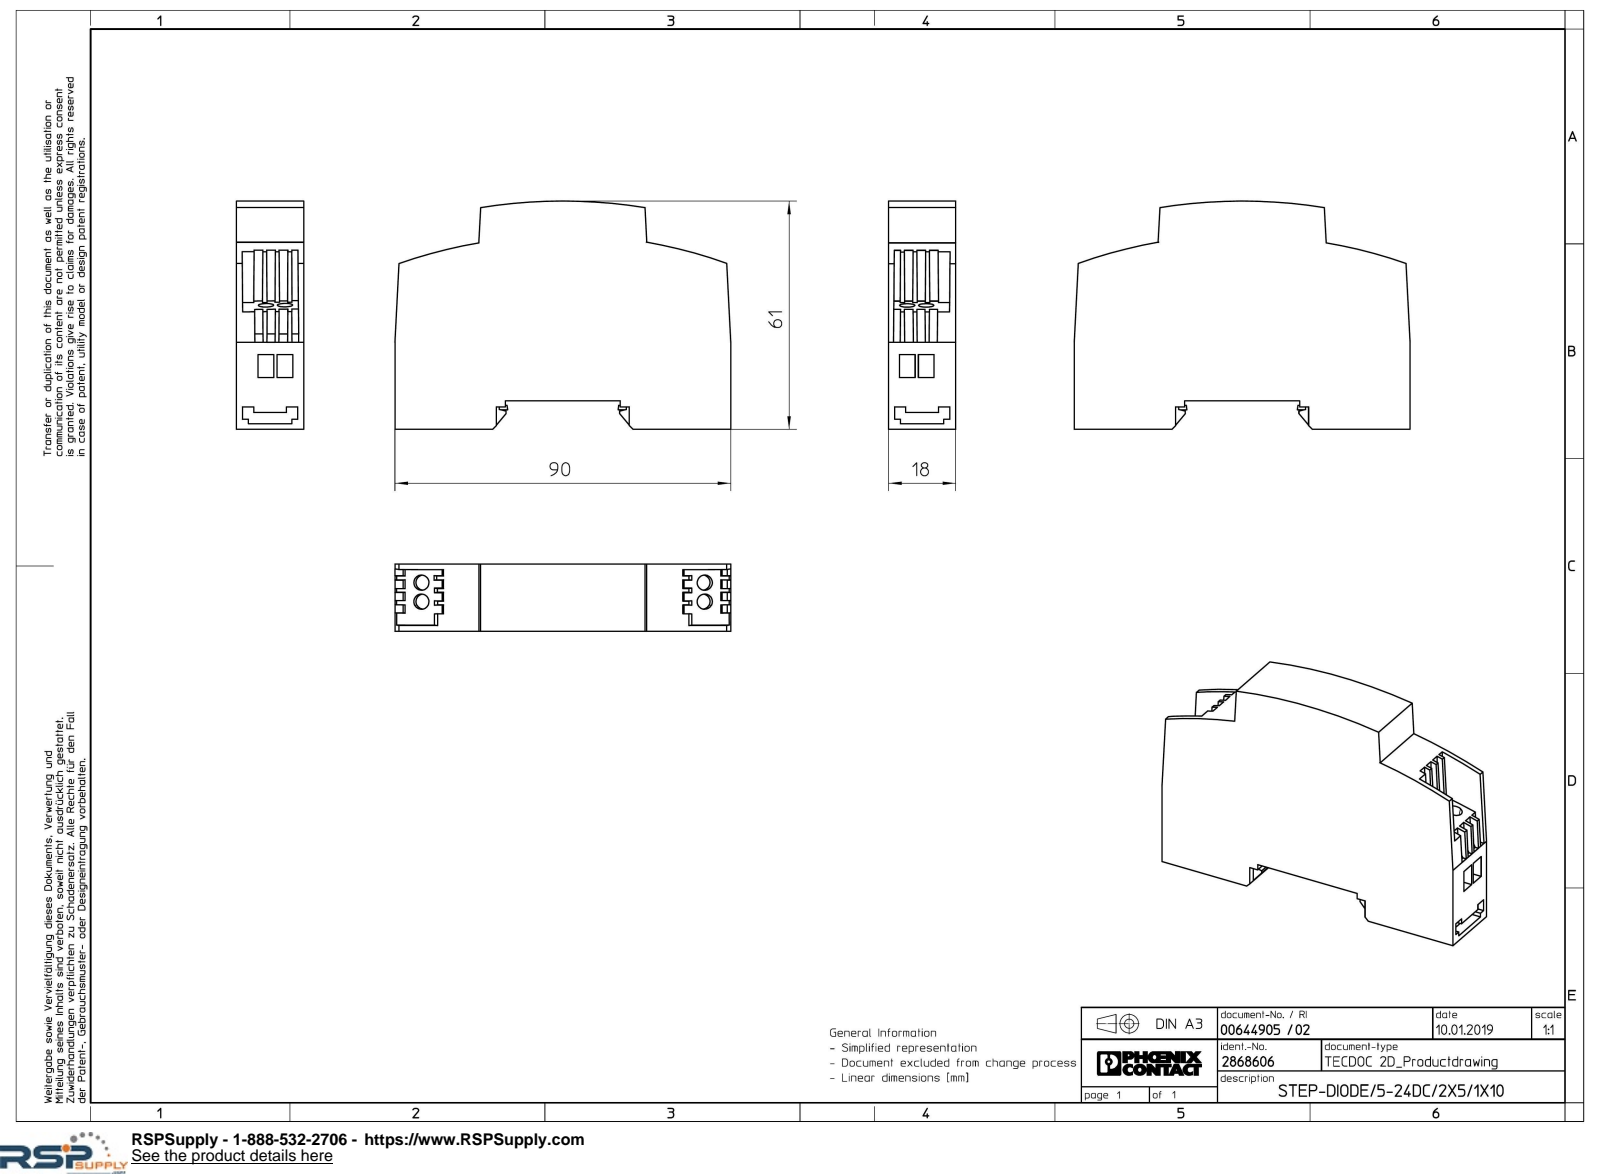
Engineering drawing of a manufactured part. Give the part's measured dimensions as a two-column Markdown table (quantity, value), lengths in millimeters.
| quantity | value |
| --- | --- |
| part name | STEP_DIODE_5_24_DC_2x5_1x10-select |
| STEP written by | Creo Elements/Direct Modeling 20.1A 29-Sep-2018 (C) Parametric Technology GmbH (AUTOMOTIVE_DESIGN) |
| units | millimeters |
| bodies | 1 solid, 181 faces (168 planar, 5 cylindrical, 8 other) |
| overall size | 90 × 61 × 18 |
| volume | 76 738 mm³ |
| surface area | 16 487 mm² |
| partial cylindrical surfaces (radius × count) | 129.98 × 2, 119 × 1, 119 × 1, 140 × 1 |
| main face-to-face distances | 18, 7.6, 90, 3, 14.95, 3.36, 87, 1.6, 9.93, 1.5 |
